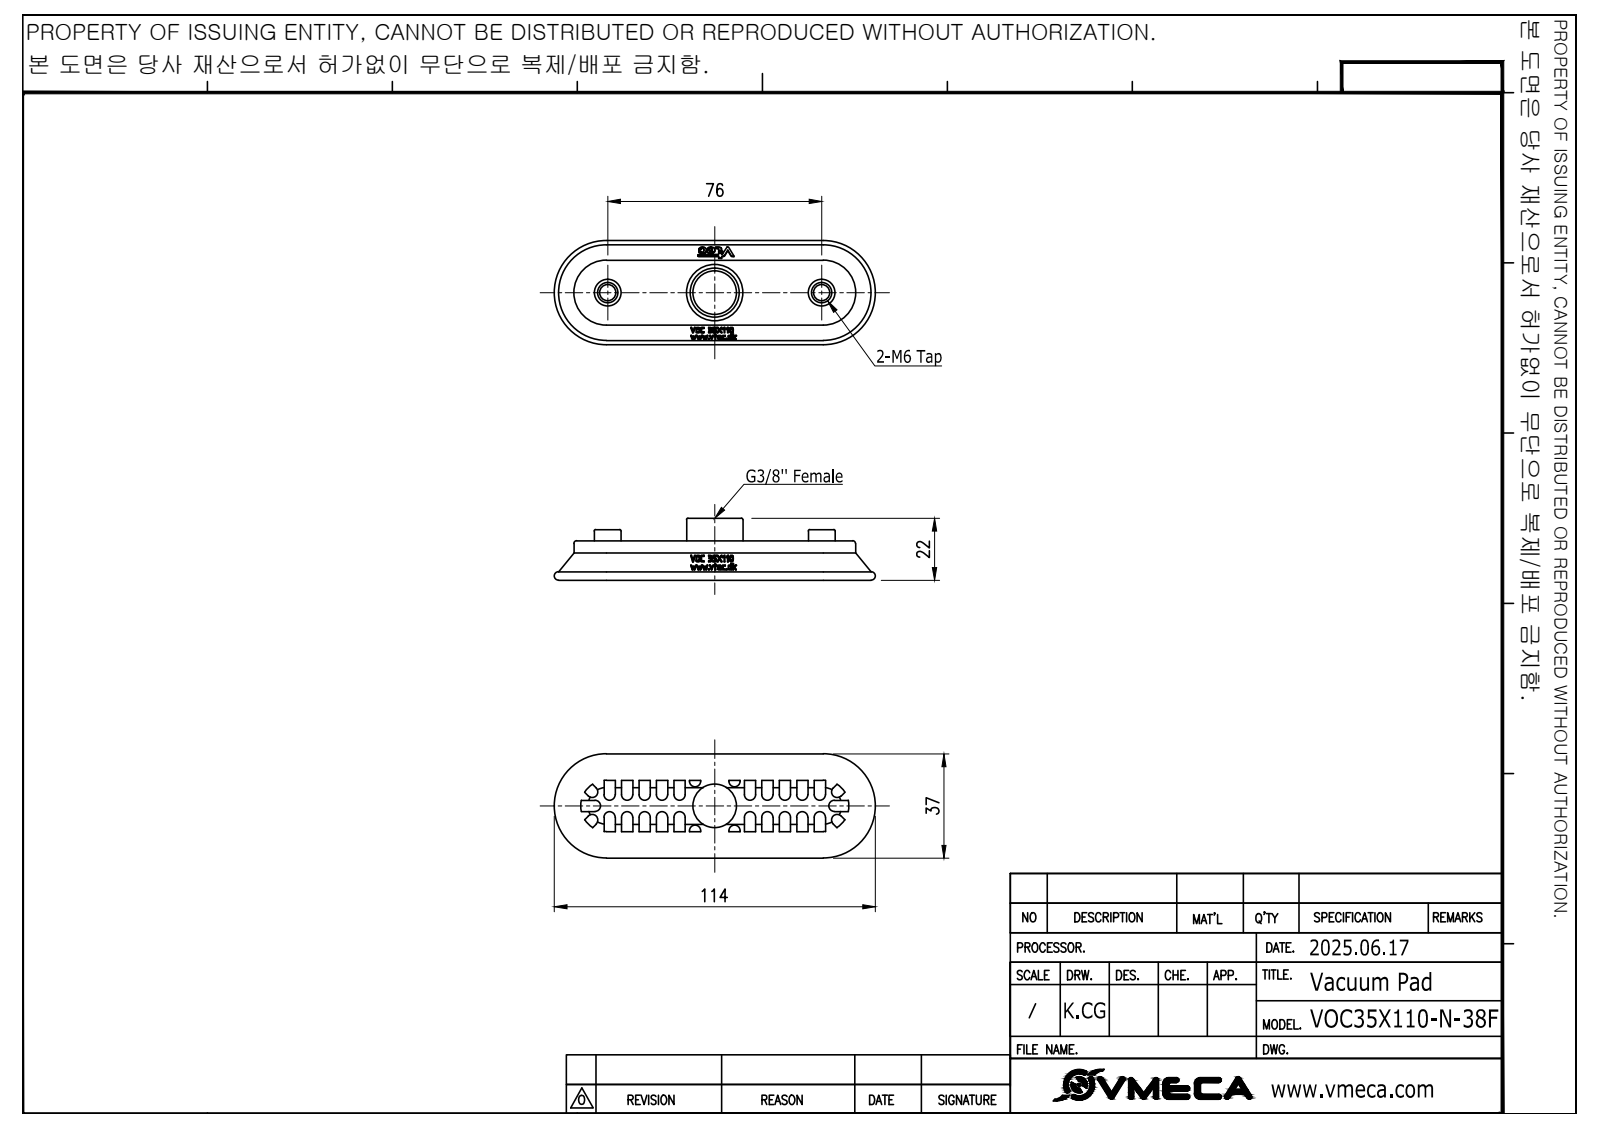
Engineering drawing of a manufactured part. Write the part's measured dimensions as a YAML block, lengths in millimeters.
step_written_by: "XStep 1.0 (CONFIG_CONTROL_DESIGN) ( ))"
units: millimeters
bodies: {solids: 1, faces: 402, planar: 153, cylindrical: 77, other: 172}
overall_size: [114, 37, 22]
volume: 24280
surface_area: 12382
round_holes:
  - {diameter: 5.8, count: 2}
  - {diameter: 15.4, count: 1}
round_bosses_or_shafts:
  - {diameter: 9.5, count: 2}
  - {diameter: 20, count: 1}
  - {diameter: 1, count: 1}
partial_cylinders:
  - {radius: 2, count: 30}
  - {radius: 0.2, count: 3}
  - {radius: 0.22, count: 3}
  - {radius: 0.34, count: 3}
  - {radius: 0.39, count: 3}
  - {radius: 0.47, count: 3}
  - {radius: 0.49, count: 3}
  - {radius: 0.62, count: 2}
face_to_face_distances: [8.4, 2, 6.4, 23, 6.2, 4, 12.4, 49.8, 16.4, 2.2]
hole_center_spacings: [38, 76]
